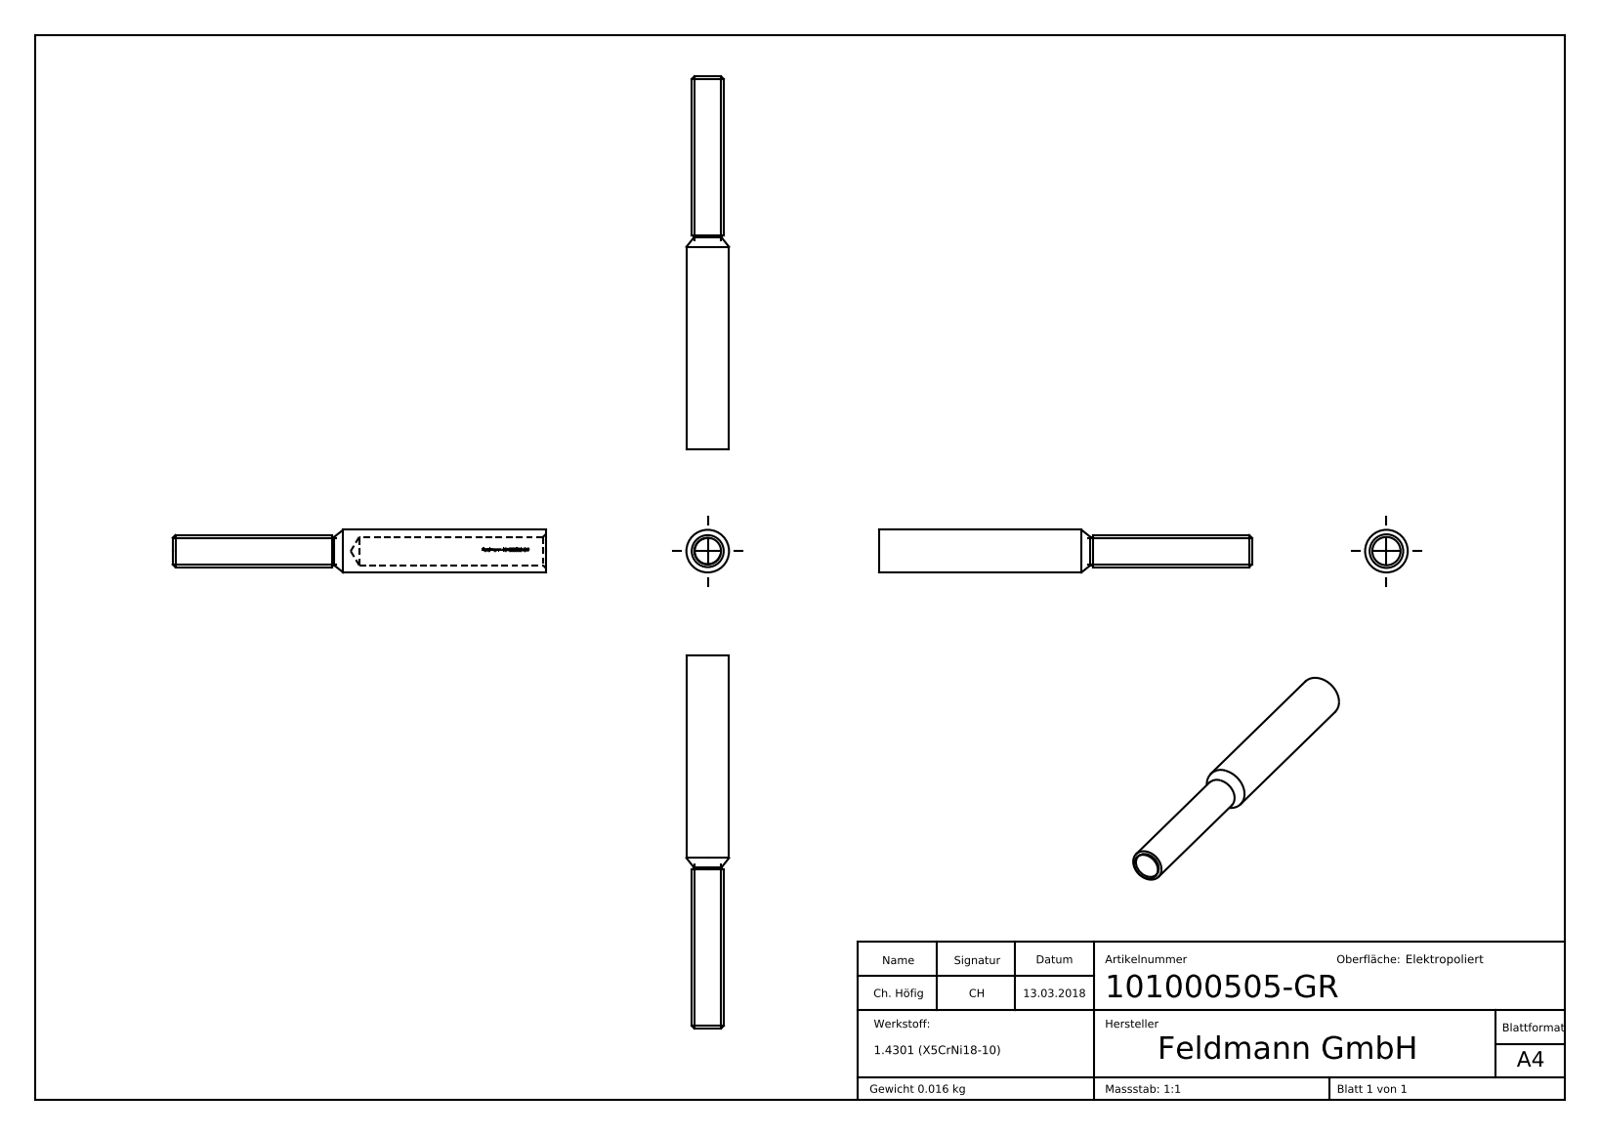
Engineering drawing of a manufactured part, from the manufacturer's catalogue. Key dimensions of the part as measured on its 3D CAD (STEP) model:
Part name (STEP PRODUCT): 101000505-GR
STEP written by: SolidWorks 2015 (CONFIG_CONTROL_DESIGN)
Units: millimetres
Bodies: 1 solid, 268 faces (100 planar, 37 cylindrical, 131 other)
Overall size (bounding box): 70 × 8 × 8
Volume: 2 036 mm³ · Surface area: 2 236 mm²
Round holes (diameter × count): ⌀5.3 ×1
Round bosses / shafts (diameter × count): ⌀8 ×1, ⌀6 ×1
Partial cylindrical surfaces — rounded edges, fillets, slot ends (radius × count): R2.75 ×1
Main face-to-face distances: 70, 40.1, 29.9, 0.81, 3.88, 3.93, 8.31, 4.43, 3.62, 4.69
